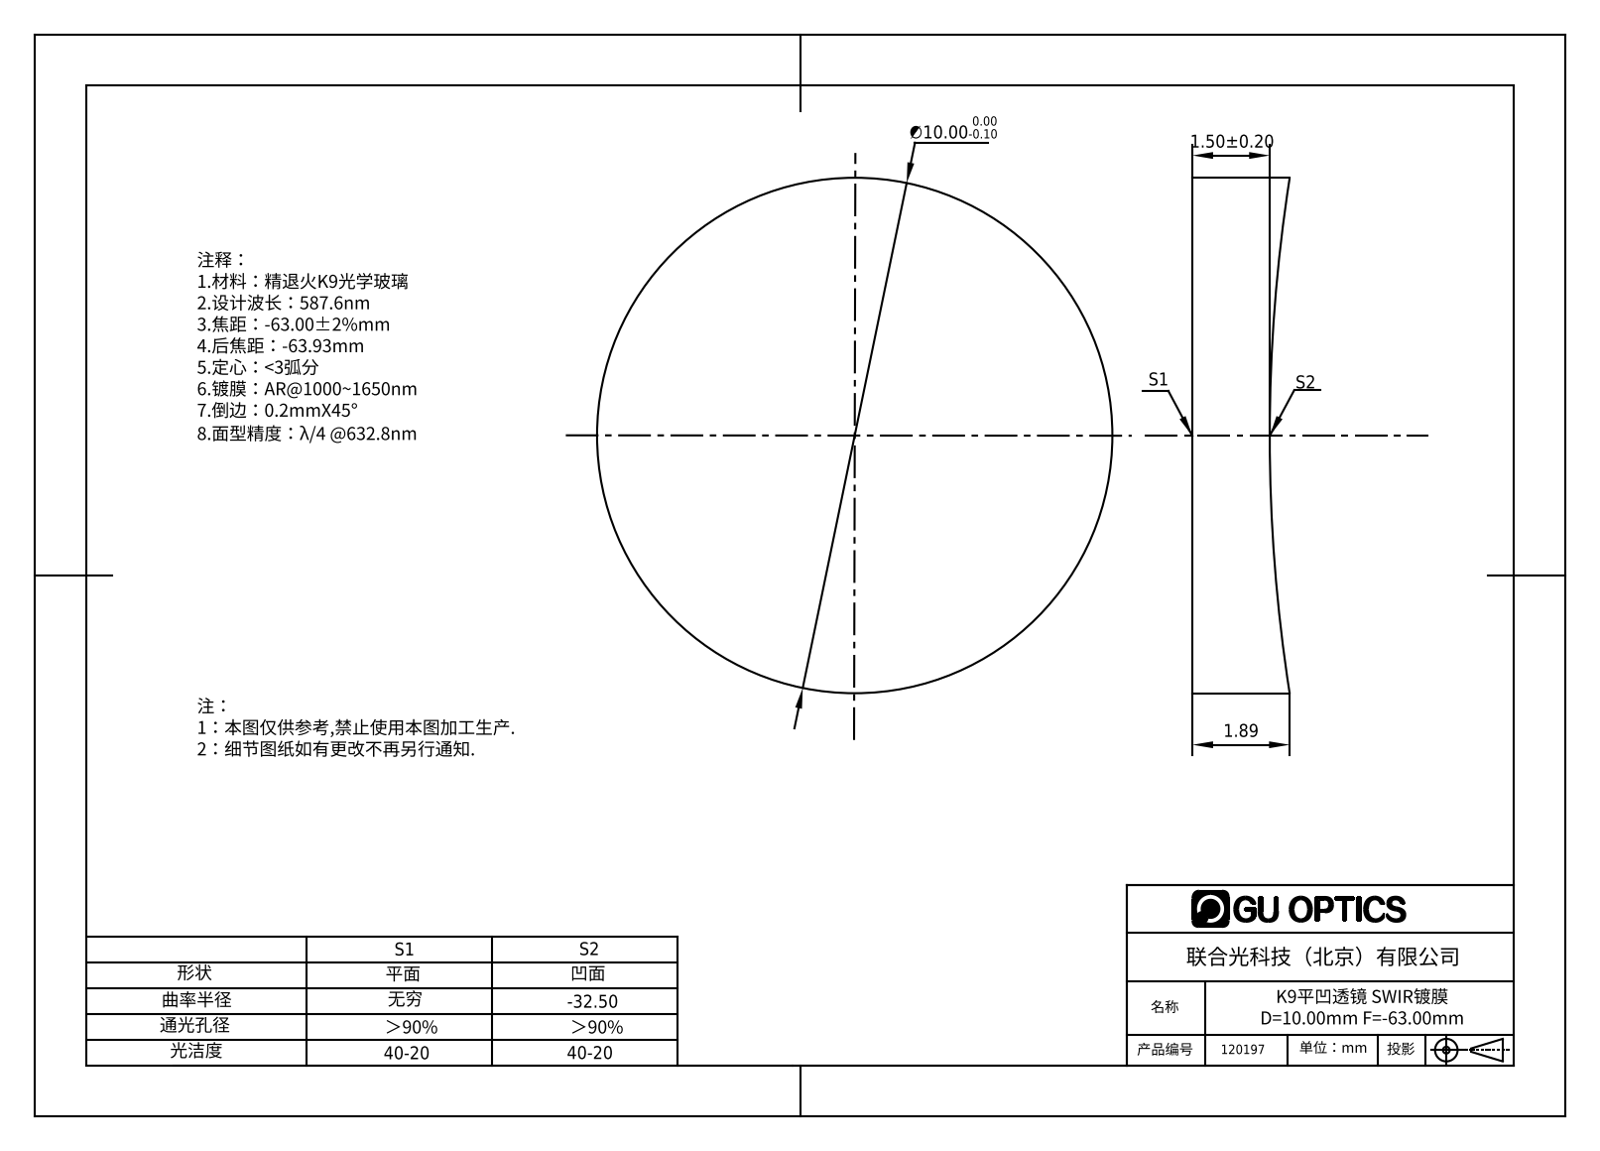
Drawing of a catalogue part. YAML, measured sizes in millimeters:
part_name: "120137"
step_written_by: "SolidWorks 2016 (AUTOMOTIVE_DESIGN)"
units: millimeters
bodies: {solids: 1, faces: 5, planar: 1, cylindrical: 2, other: 2}
overall_size: [10, 10, 1.89]
volume: 133
surface_area: 217
round_bosses_or_shafts:
  - {diameter: 10, count: 1}
